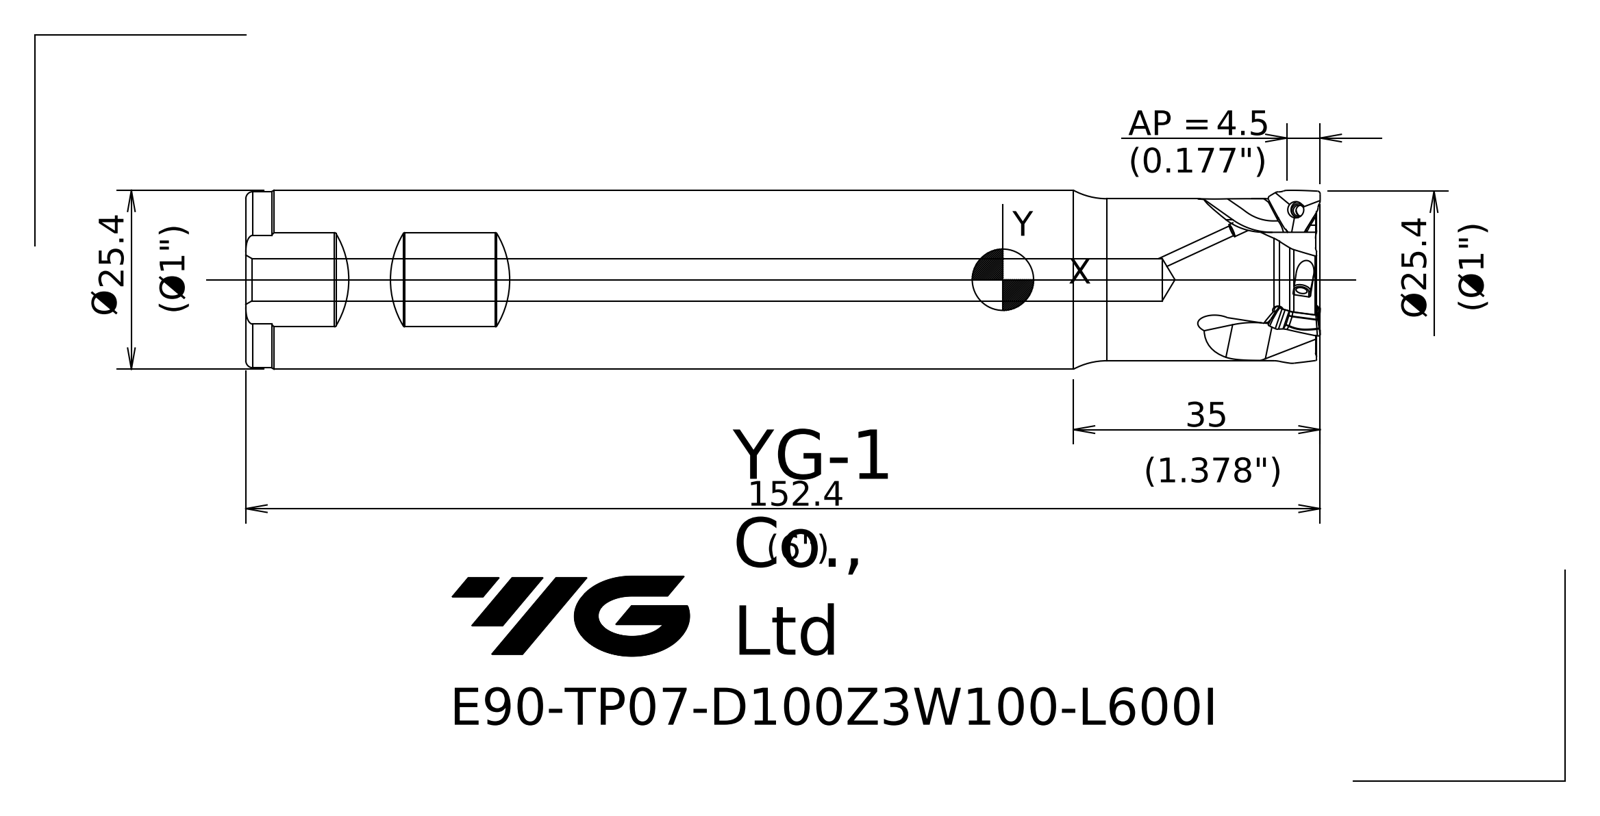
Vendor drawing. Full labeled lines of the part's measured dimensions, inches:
Part name (STEP PRODUCT): 102203D07F77yq7c
STEP written by: SIEMENS PLM Software NX 10.0 (AP203_CONFIGURATION_CONTROLLED_3D_DESIGN_OF_MECHANICAL_PARTS_AND_ASSEMBLIES_MIM_LF)
Units: inches
Bodies: 1 solid, 51 faces (8 planar, 8 cylindrical, 35 other)
Overall size (bounding box): 6 × 1.002 × 1.002
Volume: 4.26 in³ · Surface area: 25.86 in²
Round holes (diameter × count): ⌀0.059 ×1, ⌀0.236 ×1
Round bosses / shafts (diameter × count): ⌀1 ×1, ⌀0.984 ×1, ⌀0.906 ×1
Partial cylindrical surfaces — rounded edges, fillets, slot ends (radius × count): R0.012 ×3
Main face-to-face distances: 5.974, 5.98, 0.635
